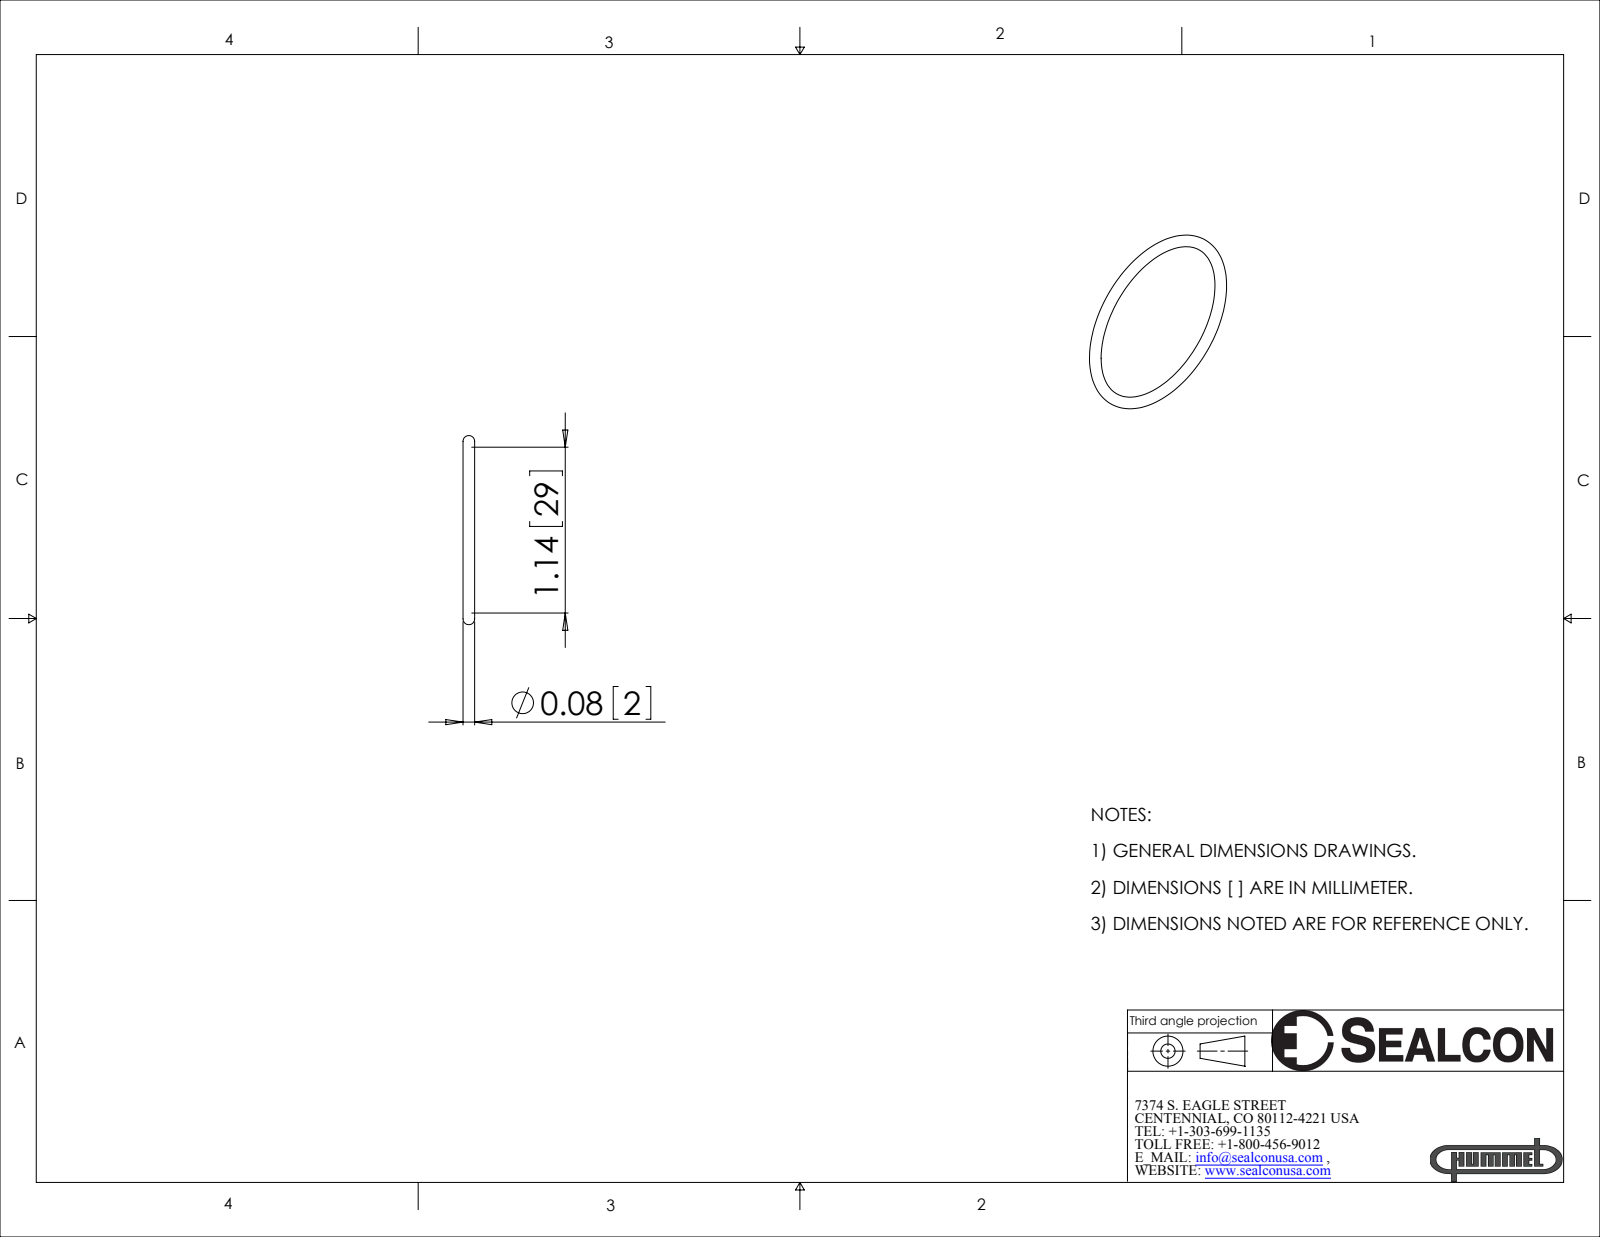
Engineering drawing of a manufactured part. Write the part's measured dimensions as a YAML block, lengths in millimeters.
part_name: "OM-32-SI"
step_written_by: "SolidWorks 2008 (CONFIG_CONTROL_DESIGN)"
units: millimeters
bodies: {solids: 1, faces: 4, planar: 0, cylindrical: 0, other: 4}
overall_size: [33, 33, 2]
volume: 310
surface_area: 621
